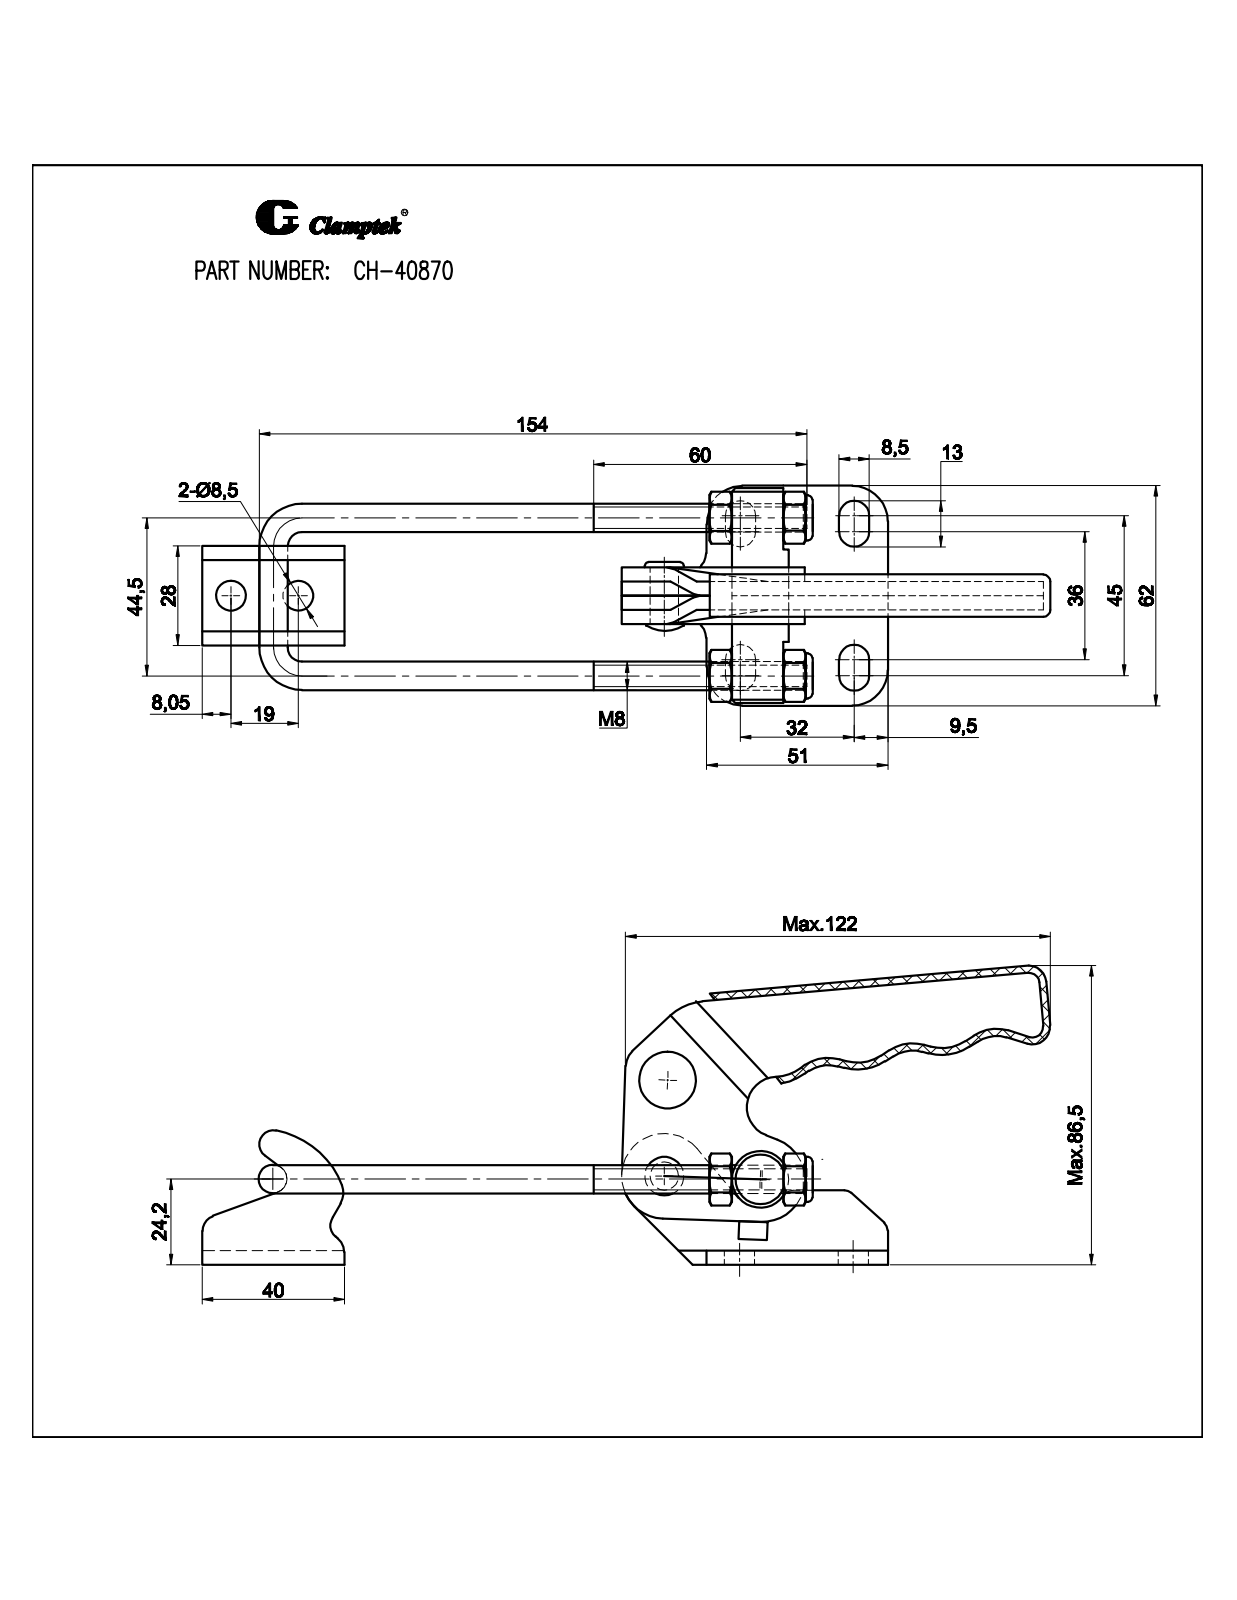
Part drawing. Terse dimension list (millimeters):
name: M8防松_默认; CH-40870
written by: SolidWorks 2008 (CONFIG_CONTROL_DESIGN)
unit: mm
bodies: 15 solids, 973 faces (316 planar, 412 cylindrical, 245 other)
size: 227.01 × 84.53 × 62
volume: 94 174 mm³; area: 64 792 mm²
holes: 4× ⌀6.5, 2× ⌀8, 2× ⌀8.3, 2× ⌀8.5, 2× ⌀16, 1× ⌀1.08, 1× ⌀5.94
bosses: 2× ⌀11, 2× ⌀8, 1× ⌀15.8, 1× ⌀0.96
rounds: 16× R1.5, 14× R4, 8× R4.25, 8× R12, 5× R3, 4× R10, 3× R4.5, 3× R5
face distances: 4, 8, 9.5, 5.5, 1.5, 12, 11, 2.5, 13.5, 17
hole spacings: 44.5, 27, 19, 38.18, 99.41, 103.93, 121.44, 126.4
